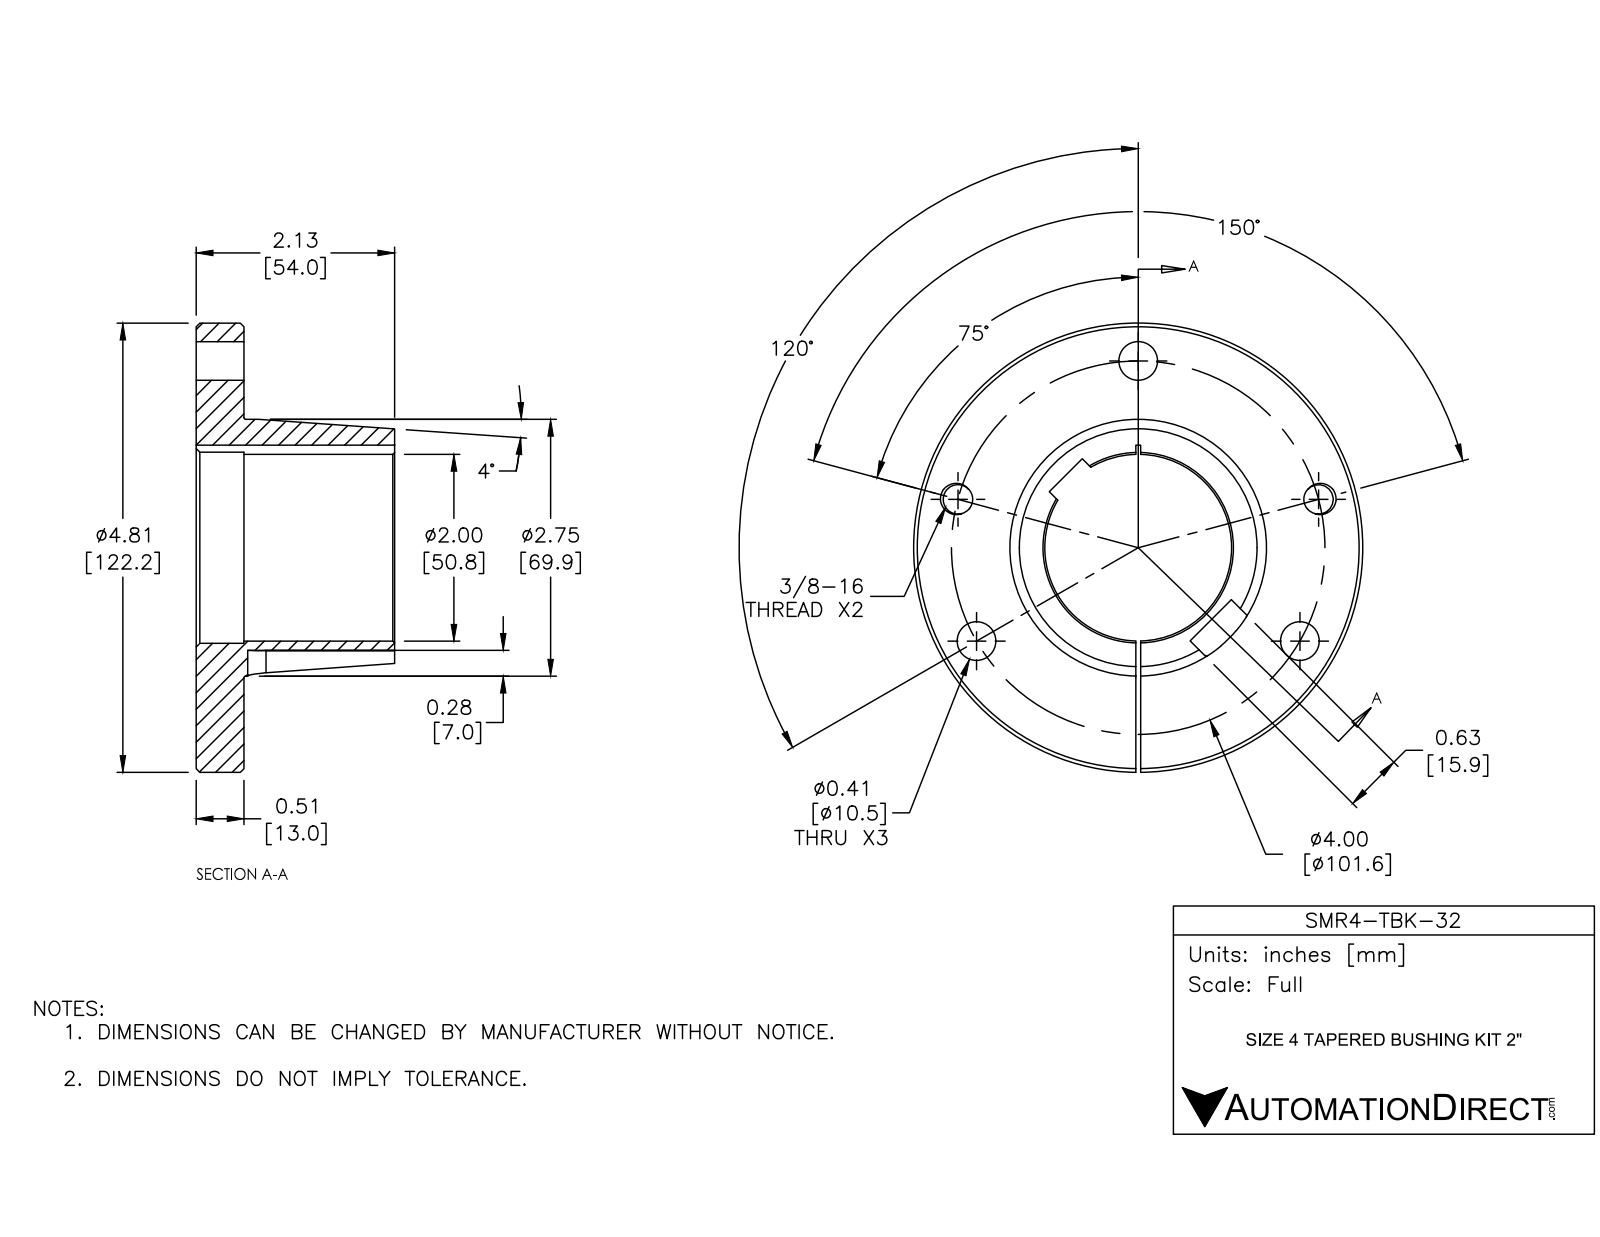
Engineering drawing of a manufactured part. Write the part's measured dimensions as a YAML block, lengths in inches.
part_name: "SMR4-TBK-32"
step_written_by: "SolidWorks 2016 (AUTOMOTIVE_DESIGN)"
units: inches
bodies: {solids: 1, faces: 137, planar: 18, cylindrical: 96, other: 23}
overall_size: [4.811, 4.811, 2.126]
volume: 10.79
surface_area: 69
round_holes:
  - {diameter: 0.413, count: 3}
  - {diameter: 0.315, count: 2}
  - {diameter: 0.375, count: 2}
  - {diameter: 2, count: 1}
  - {diameter: 2.047, count: 1}
round_bosses_or_shafts:
  - {diameter: 4.811, count: 1}
  - {diameter: 2.75, count: 1}
partial_cylinders:
  - {radius: 0.197, count: 2}
face_to_face_distances: [0.512, 2.126, 1.614, 0.051, 2.196, 0.063, 0.563, 0.5, 0.625, 0.551]
hole_center_spacings: [2, 1.531, 2.435, 3.464, 3.966, 3.464, 3.864]
